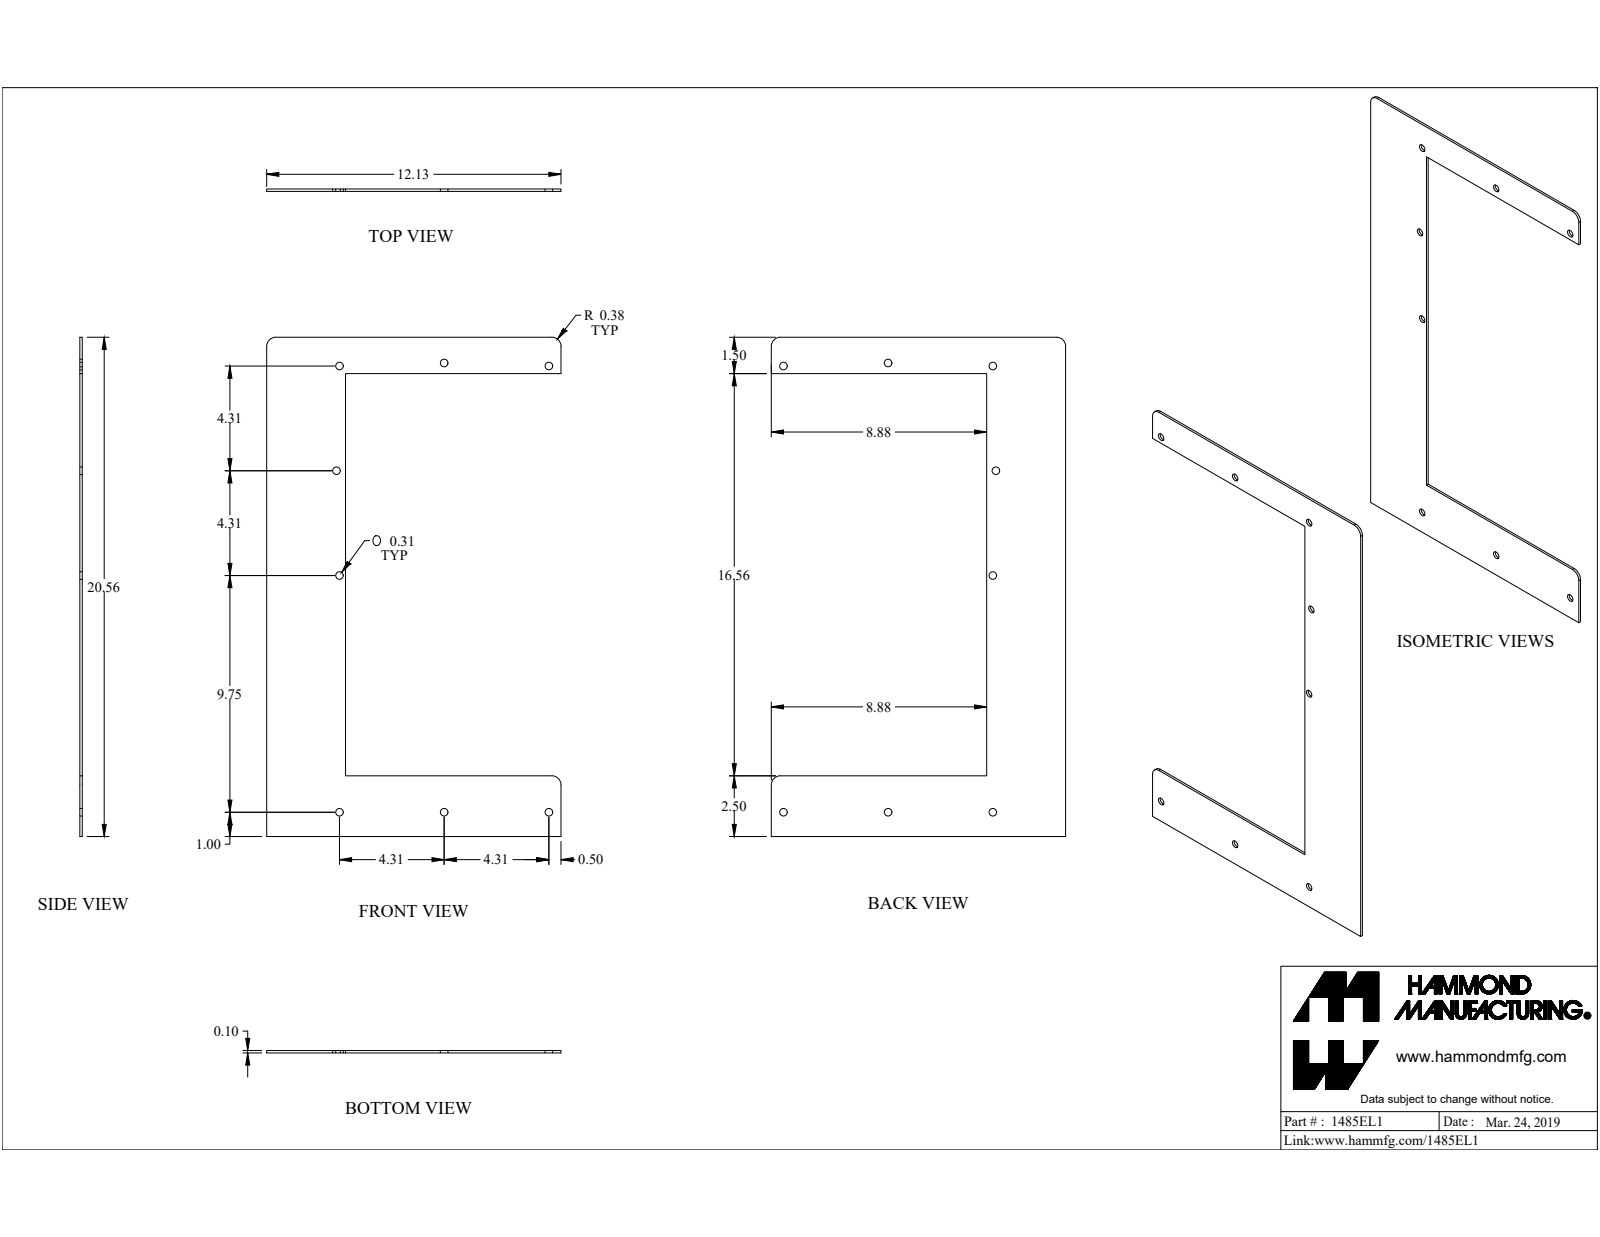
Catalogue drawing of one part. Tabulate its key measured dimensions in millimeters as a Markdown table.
| quantity | value |
| --- | --- |
| part name | 1485EL1 |
| STEP written by | SolidWorks 2019 (CONFIG_CONTROL_DESIGN) |
| units | millimeters |
| bodies | 1 solid, 21 faces (10 planar, 11 cylindrical, 0 other) |
| overall size | 522.2 × 308 × 2.5 |
| volume | 166 500 mm³ |
| surface area | 137 000 mm² |
| round holes (diameter × count) | 8 × 8 |
| partial cylindrical surfaces (radius × count) | 9.5 × 3 |
| main face-to-face distances | 2.5, 82.6, 522.2, 38.1, 484.1, 458.7, 420.6, 63.5, 308, 225.4 |
| hole center spacings | 109.6, 219.1, 466.6, 479.3, 482.4, 515.5, 109.5, 109.6 |
